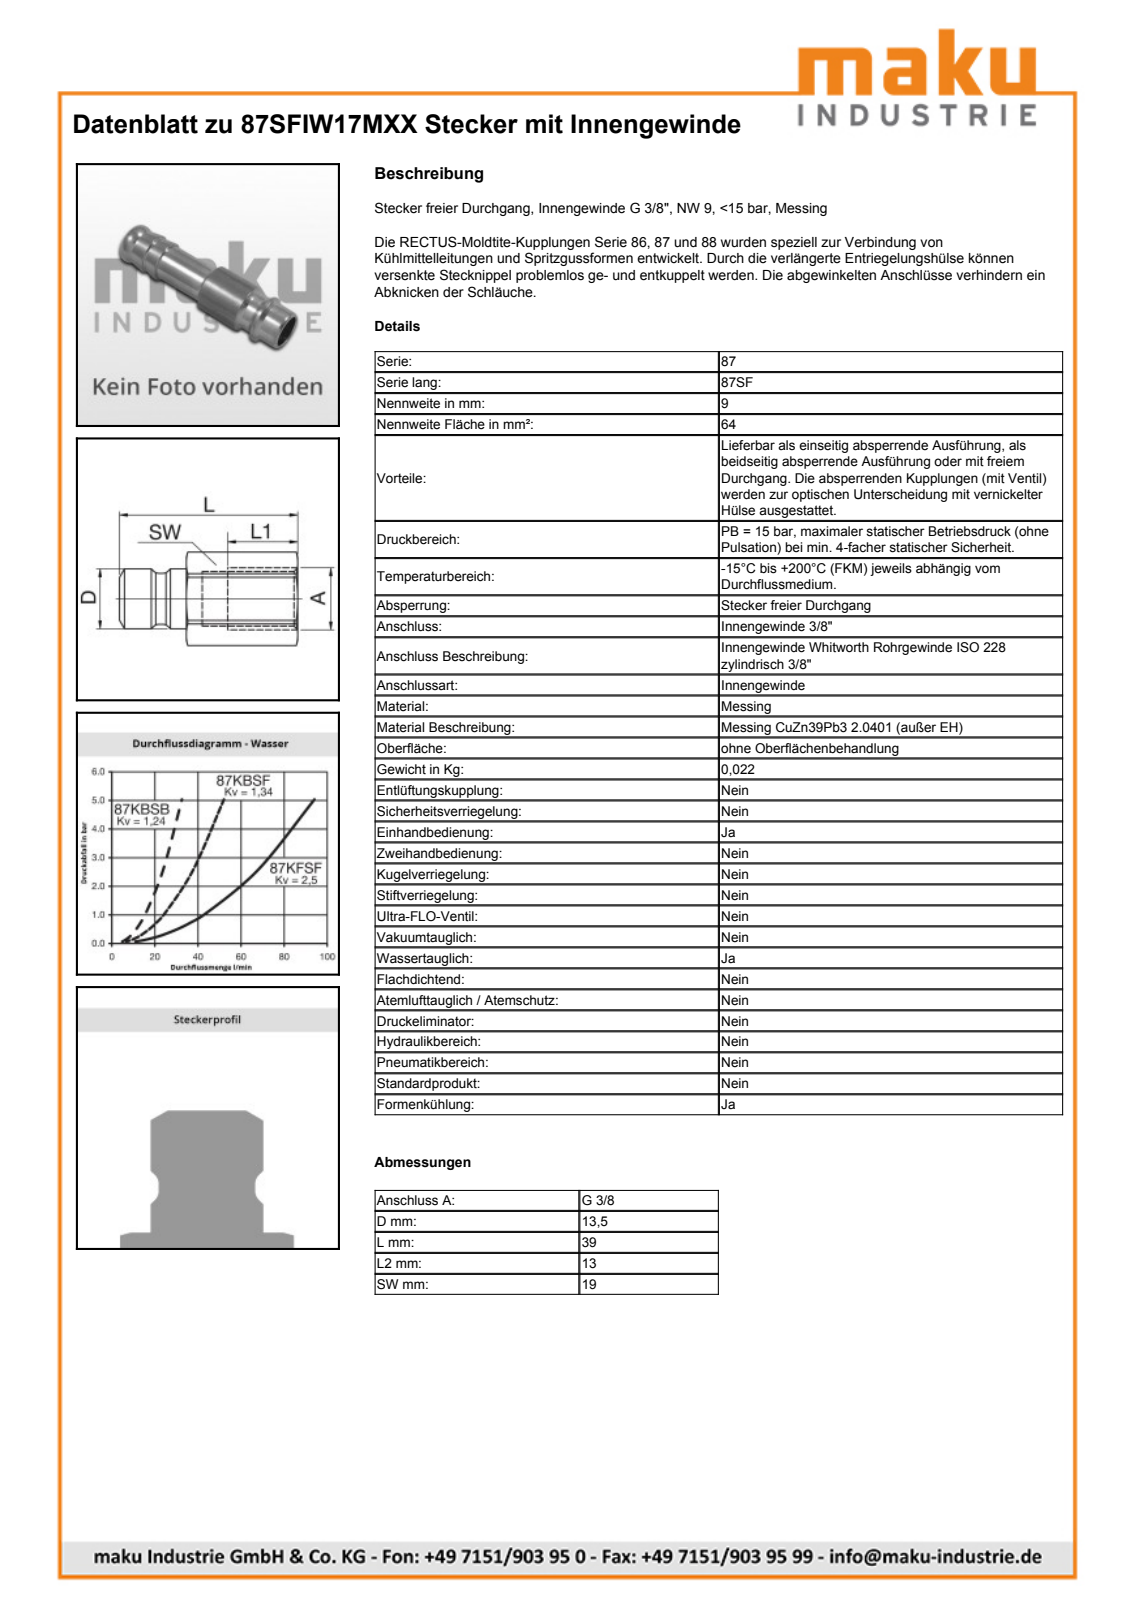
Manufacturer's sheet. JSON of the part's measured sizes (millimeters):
{"part_name": "D108468", "step_written_by": "Autodesk Inventor 2013 (AUTOMOTIVE_DESIGN)", "units": "millimeters", "bodies": {"solids": 1, "faces": 39, "planar": 10, "cylindrical": 11, "other": 18}, "overall_size": [39, 21.4, 19], "volume_mm3": 5061, "surface_area_mm2": 4040, "round_holes": [[9.2, 1], [14.95, 1]], "round_bosses_or_shafts": [[13.5, 1], [11.5, 1]], "partial_cylinders_radius": [[10.7, 1]], "face_to_face_distances": [19, 7.5, 23.5, 16, 15.5, 23, 39]}
